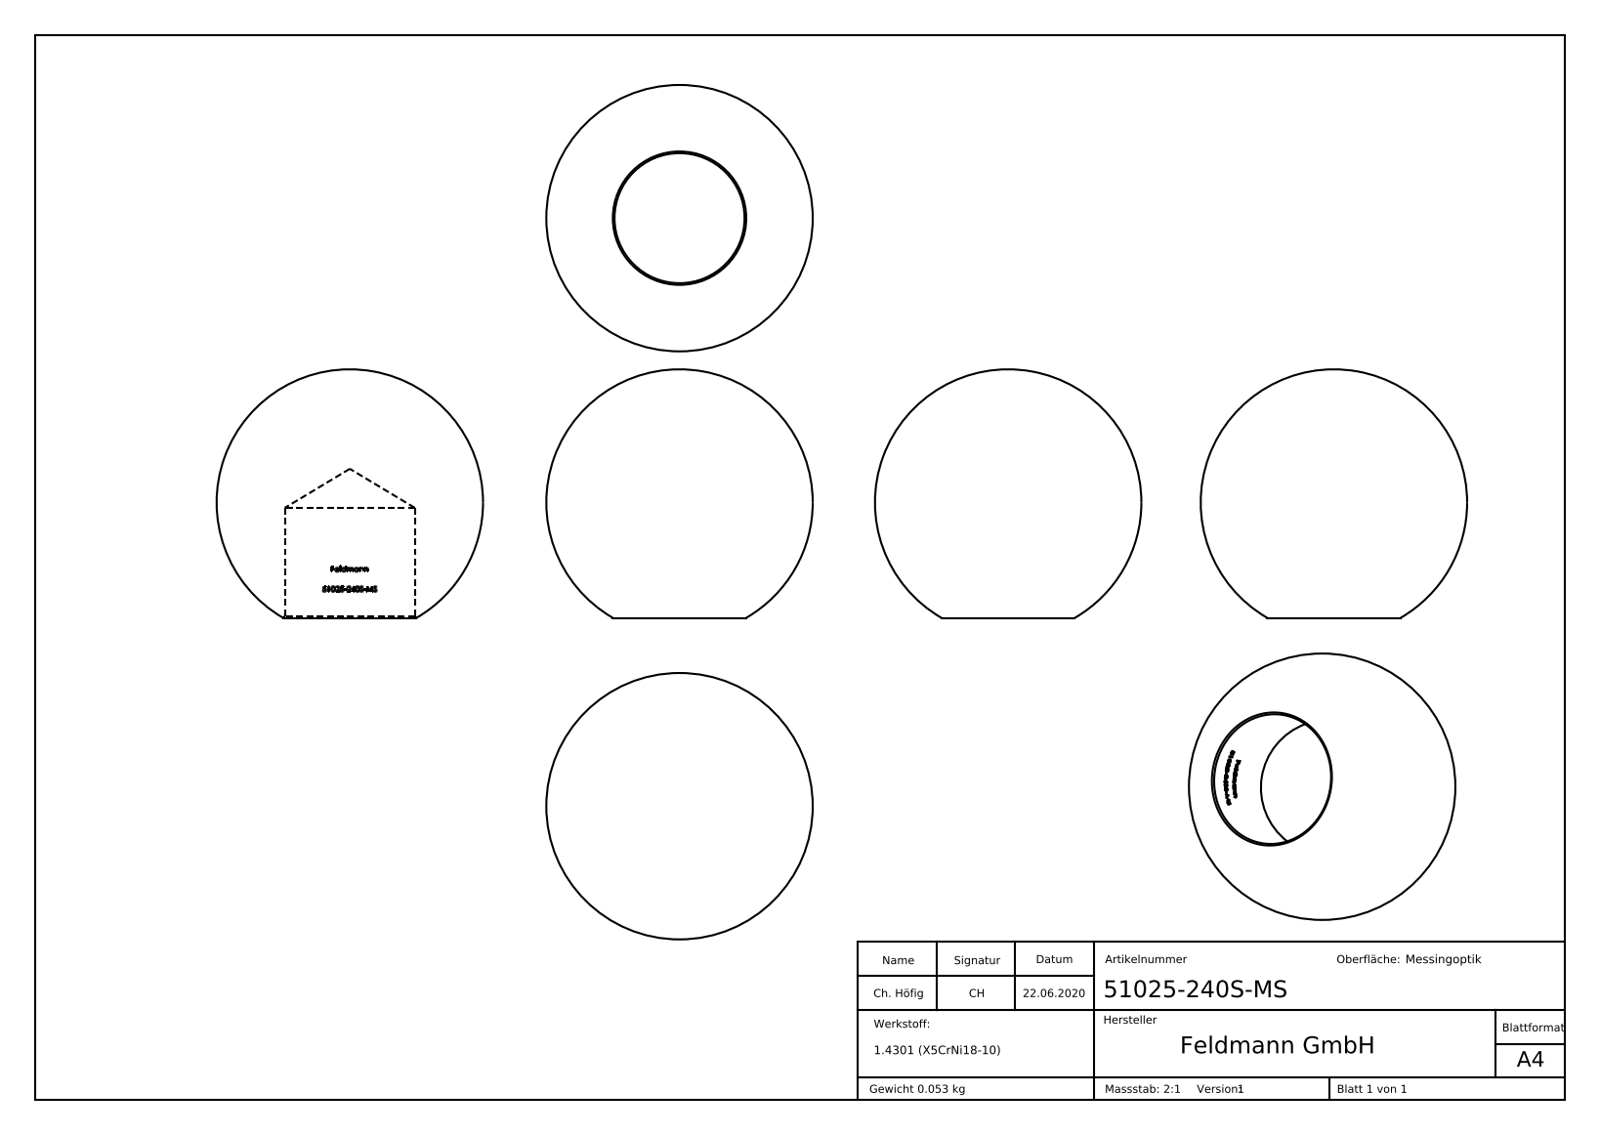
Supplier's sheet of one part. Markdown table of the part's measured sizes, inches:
| quantity | value |
| --- | --- |
| part name | 51025-240S-MS |
| STEP written by | SolidWorks 2015 (CONFIG_CONTROL_DESIGN) |
| units | inches |
| bodies | 1 solid, 277 faces (122 planar, 28 cylindrical, 127 other) |
| overall size | 0.984 × 0.984 × 0.918 |
| volume | 0.41 in³ |
| surface area | 3.675 in² |
| round holes (diameter × count) | 0.48 × 1 |
| partial cylindrical surfaces (radius × count) | 0.244 × 1 |
| main face-to-face distances | 0.053, 0.047, 0.074, 0.021, 0.072, 0.062, 0.026, 0.084, 0.022, 0.043 |
